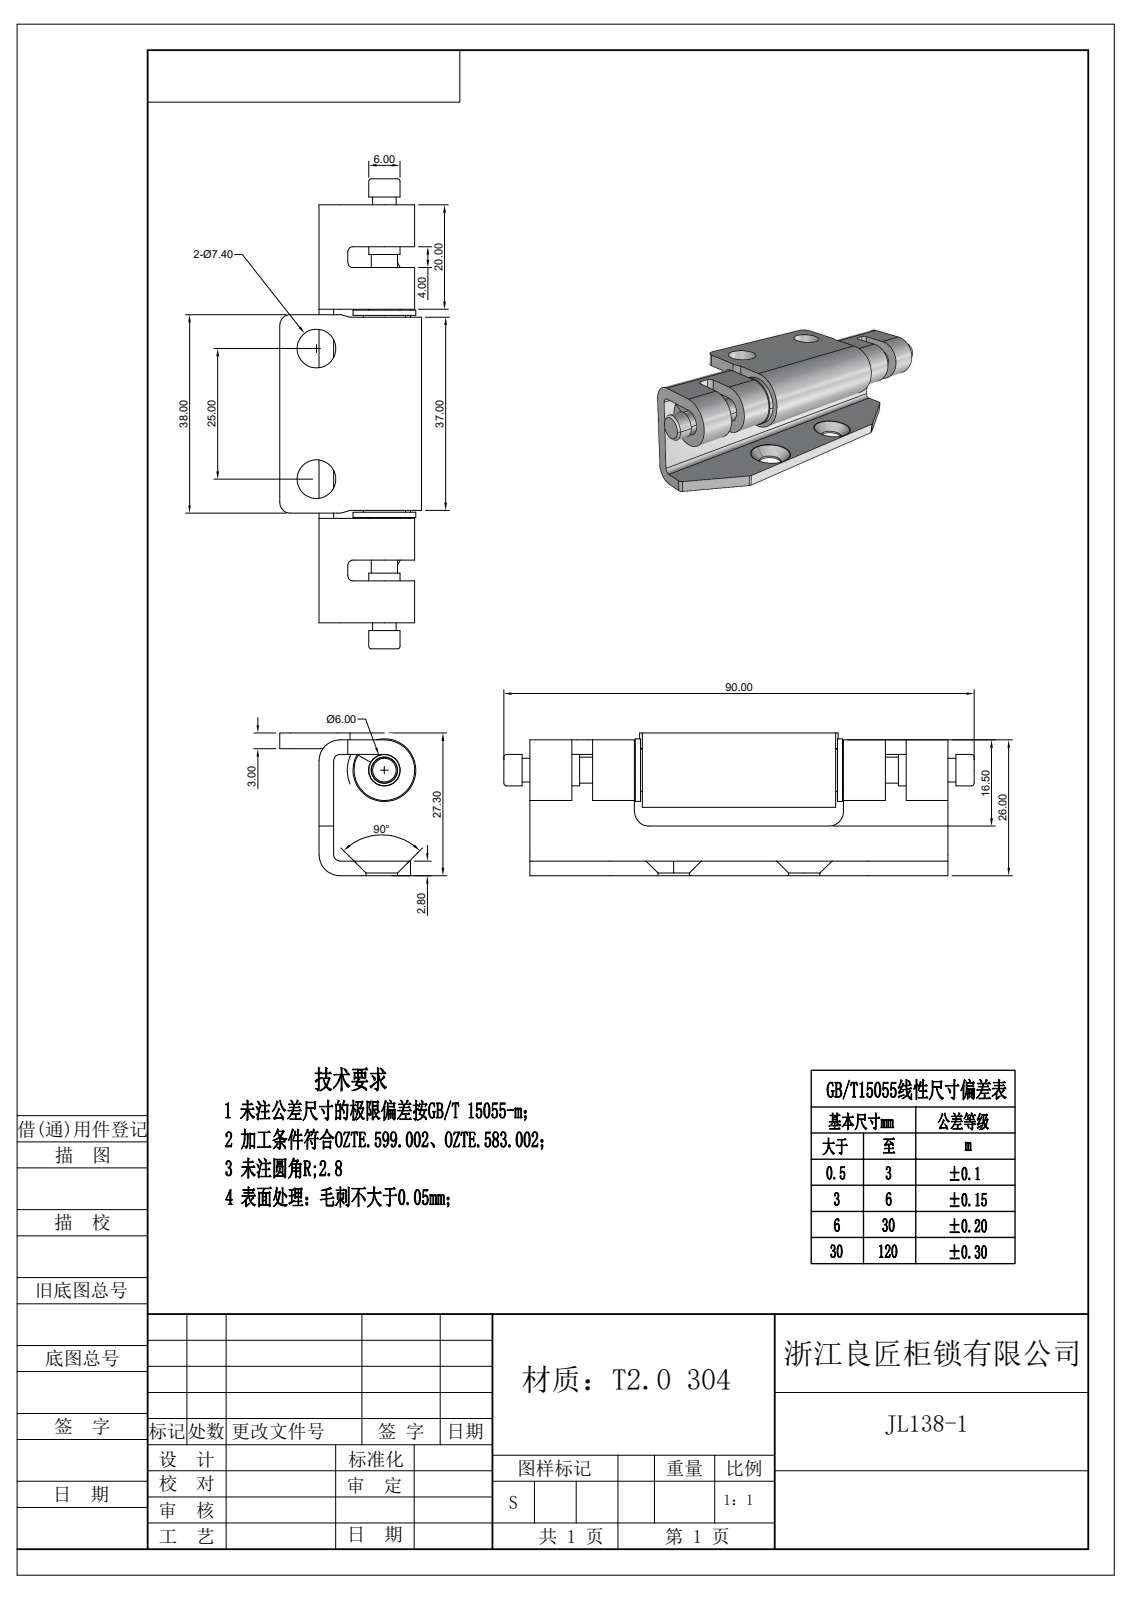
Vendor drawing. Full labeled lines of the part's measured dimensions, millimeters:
STEP written by: Rhino 8.5 (CONFIG_CONTROL_DESIGN)
Units: millimetres
Bodies: 6 solids, 168 faces (62 planar, 80 cylindrical, 26 other)
Overall size (bounding box): 90 × 27.3 × 27.1
Volume: 17 065 mm³ · Surface area: 15 138 mm²
Round holes (diameter × count): ⌀6 ×2, ⌀7.4 ×2, ⌀8.2 ×1
Round bosses / shafts (diameter × count): ⌀14.2 ×1, ⌀12 ×1, ⌀11.6 ×1, ⌀8.1 ×1, ⌀6 ×1, ⌀5 ×1, ⌀4.5 ×1
Partial cylindrical surfaces — rounded edges, fillets, slot ends (radius × count): R1 ×8, R1.2 ×2, R2 ×2, R2.8 ×2, R4 ×2
Main face-to-face distances: 2.8, 24.3, 21.5, 27.3, 24.5, 3, 23.2, 60, 8, 12
Hole centre spacings: 12.5, 25, 27.94, 27.96
